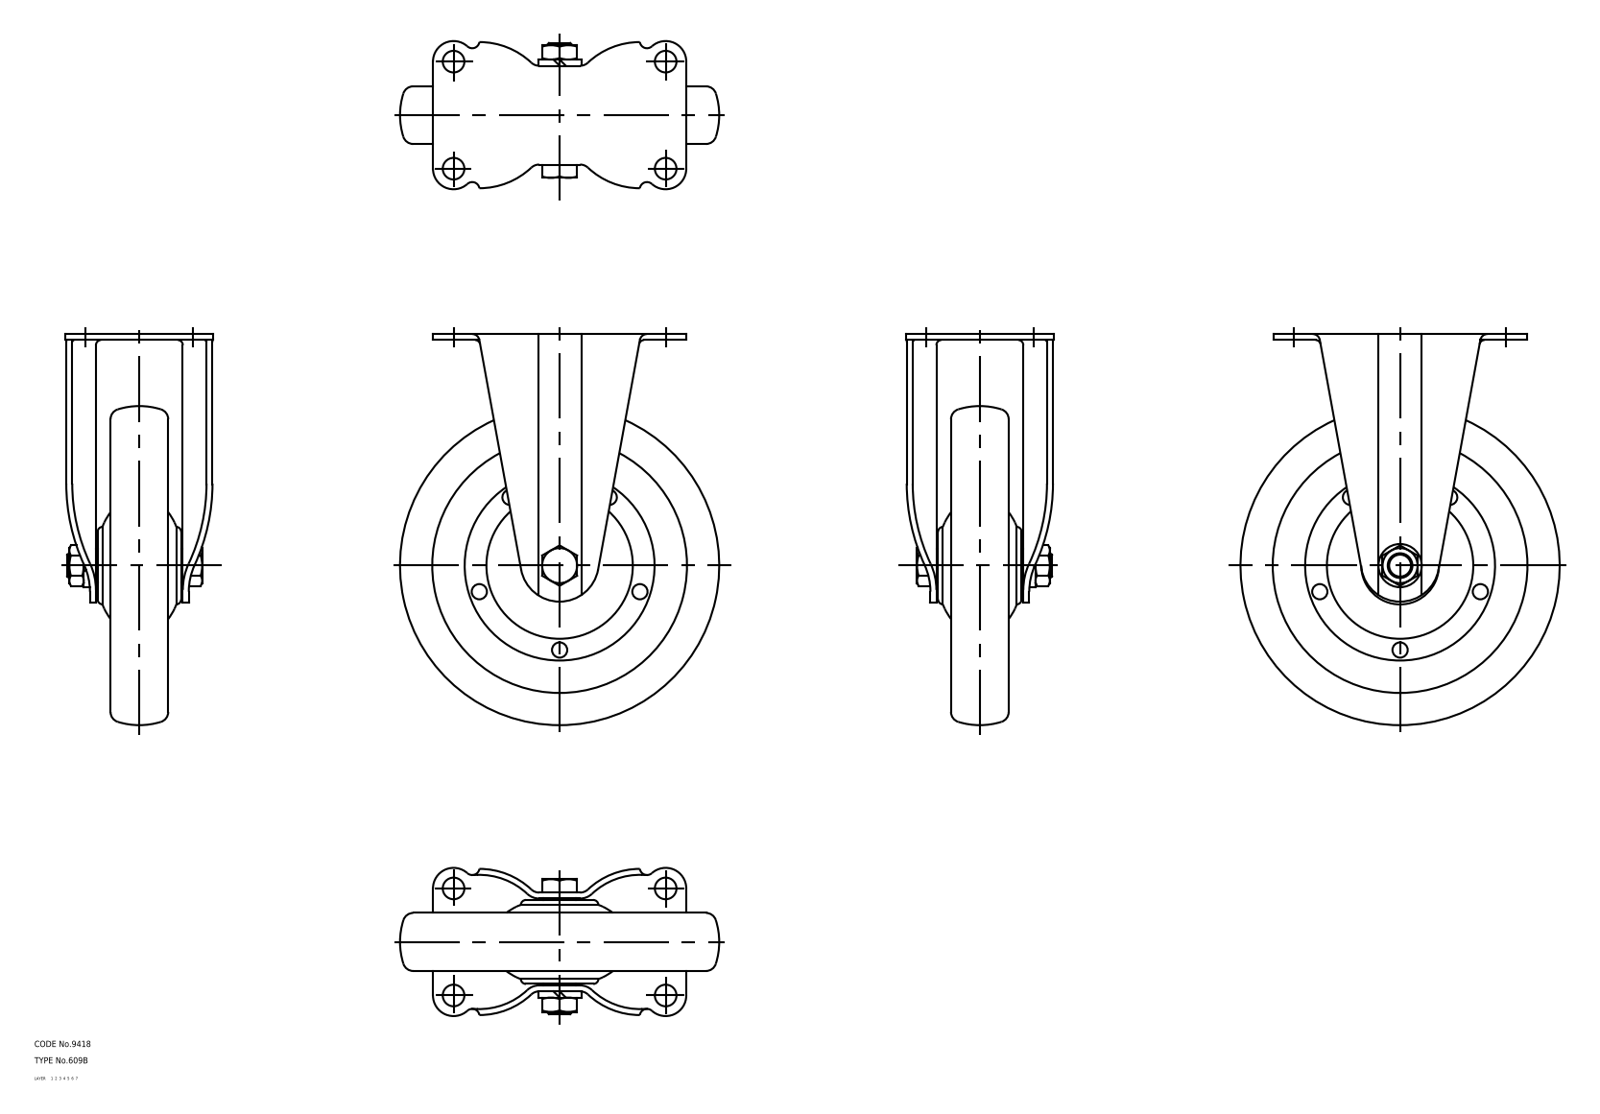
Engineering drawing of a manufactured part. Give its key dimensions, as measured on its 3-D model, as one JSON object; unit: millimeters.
{"part_name": "67121080; 67121093; 67121106", "step_written_by": "CADfix (AUTOMOTIVE_DESIGN)", "units": "millimeters", "bodies": {"solids": 3, "faces": 184, "planar": 0, "cylindrical": 0, "other": 184}, "overall_size": [190, 155, 72], "volume_mm3": 520069, "surface_area_mm2": 102972}
